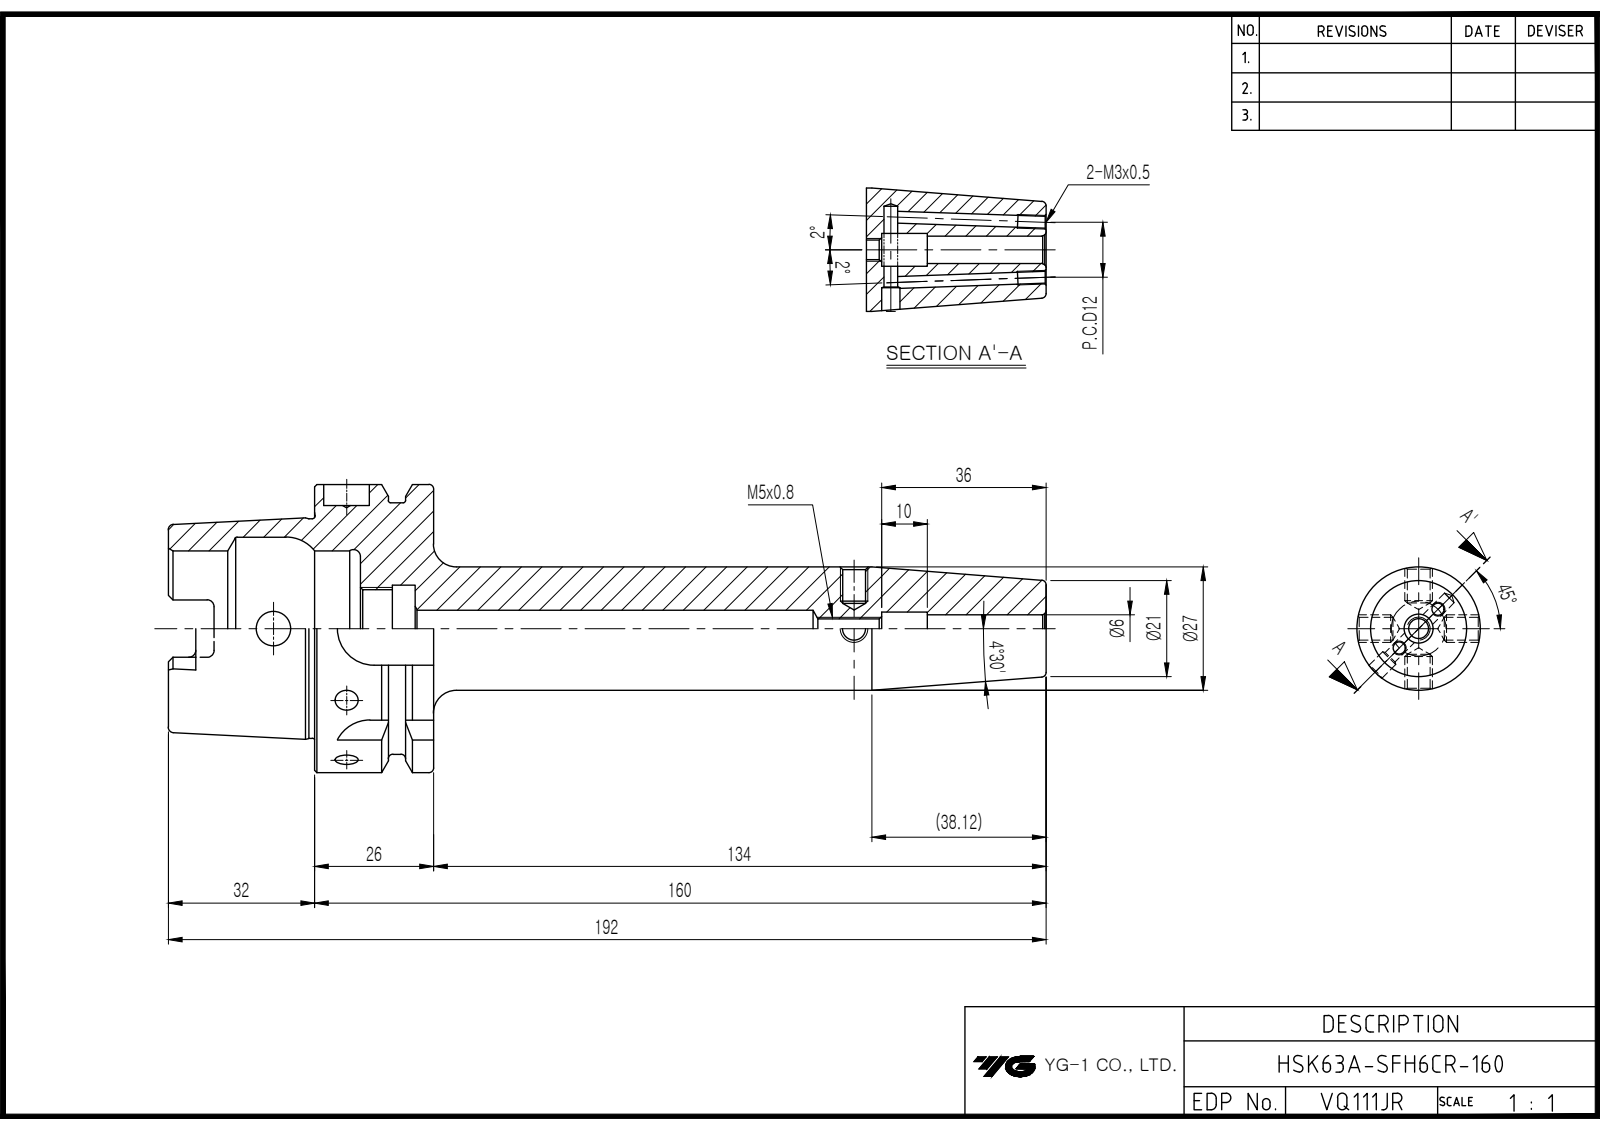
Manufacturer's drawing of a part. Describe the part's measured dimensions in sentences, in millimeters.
The part is named "LO-HSK63A-SFH6CR-160". Its 3-D file was written by "Autodesk Inventor 2022 (AUTOMOTIVE_DESIGN)". It is 1 solid with 121 faces: 42 planar, 36 cylindrical and 43 other. Overall it measures 192 by 63 by 63 millimeters. Its volume is 148 314 cubic millimeters and its surface area 36 483 square millimeters. Round holes: 2 of diameter 2.46, 1 of diameter 4.13, 1 of diameter 6, 1 of diameter 7.2, 1 of diameter 7.5, 1 of diameter 8, 1 of diameter 10, 1 of diameter 16.92, 1 of diameter 19, 1 of diameter 34, 1 of diameter 40. Round bosses or shafts: 1 of diameter 63, 1 of diameter 55, 1 of diameter 48.04, 1 of diameter 27. Partial cylindrical surfaces (rounded edges, fillets, slot ends): 6 of radius 1.5, 4 of radius 2.88, 4 of radius 8. The main face-to-face distances are 26, 10, 16, 32, 42, 58, 53, 22, 4, 12.
